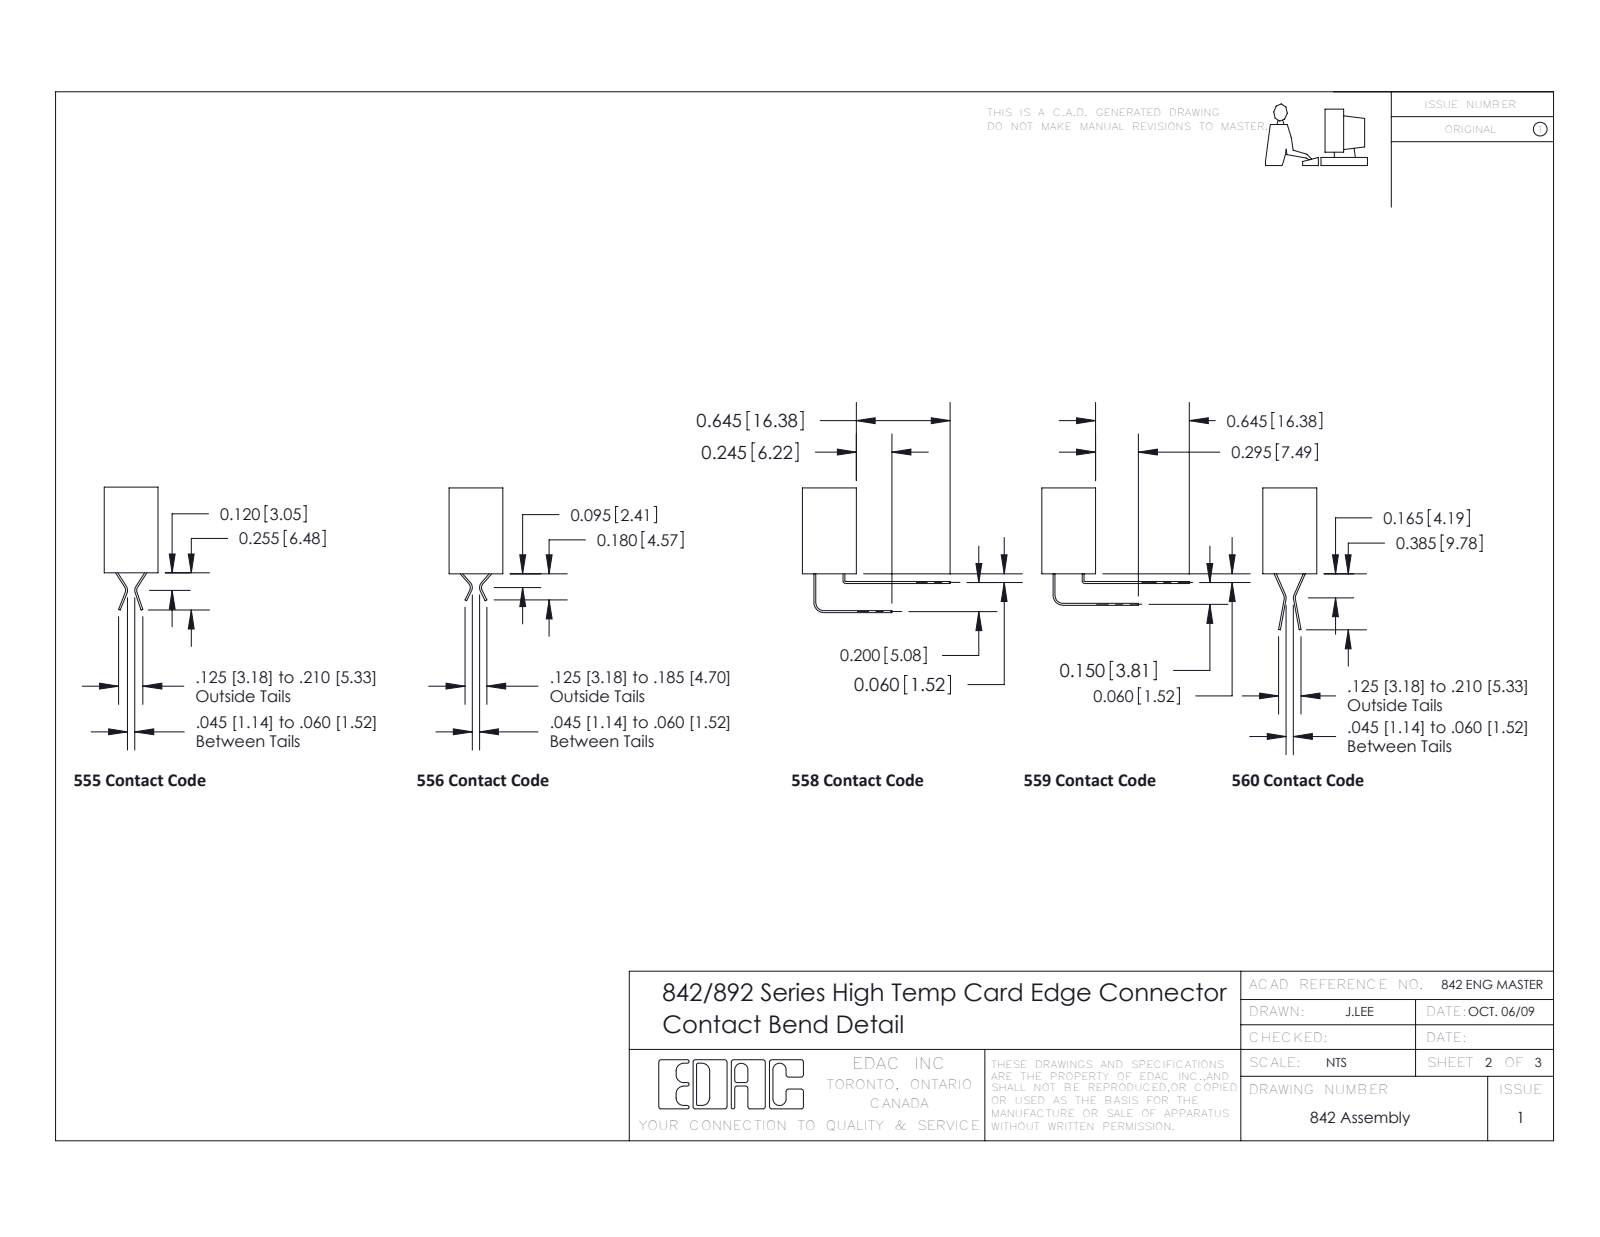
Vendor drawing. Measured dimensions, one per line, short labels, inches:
name: 345-292-001_345-293-142; 342 Part_.156 TH; 342-066-542-204
written by: SolidWorks 2016 (CONFIG_CONTROL_DESIGN)
unit: in
bodies: 67 solids, 3542 faces (2442 planar, 1100 cylindrical, 0 other)
size: 4.1 × 1.245 × 0.37
volume: 0.582 in³; area: 25.58 in²
holes: 2× ⌀0.156
rounds: 99× R0.006, 66× R0.01, 22× R0.01, 6× R0.007, 6× R0.031, 3× R0.026, 2× R0.014, 2× R0.022
face distances: 0.072, 0.298, 0.2, 0.098, 0.272, 0.025, 0.225, 0.37, 0.076, 0.175
hole spacings: 3.822
